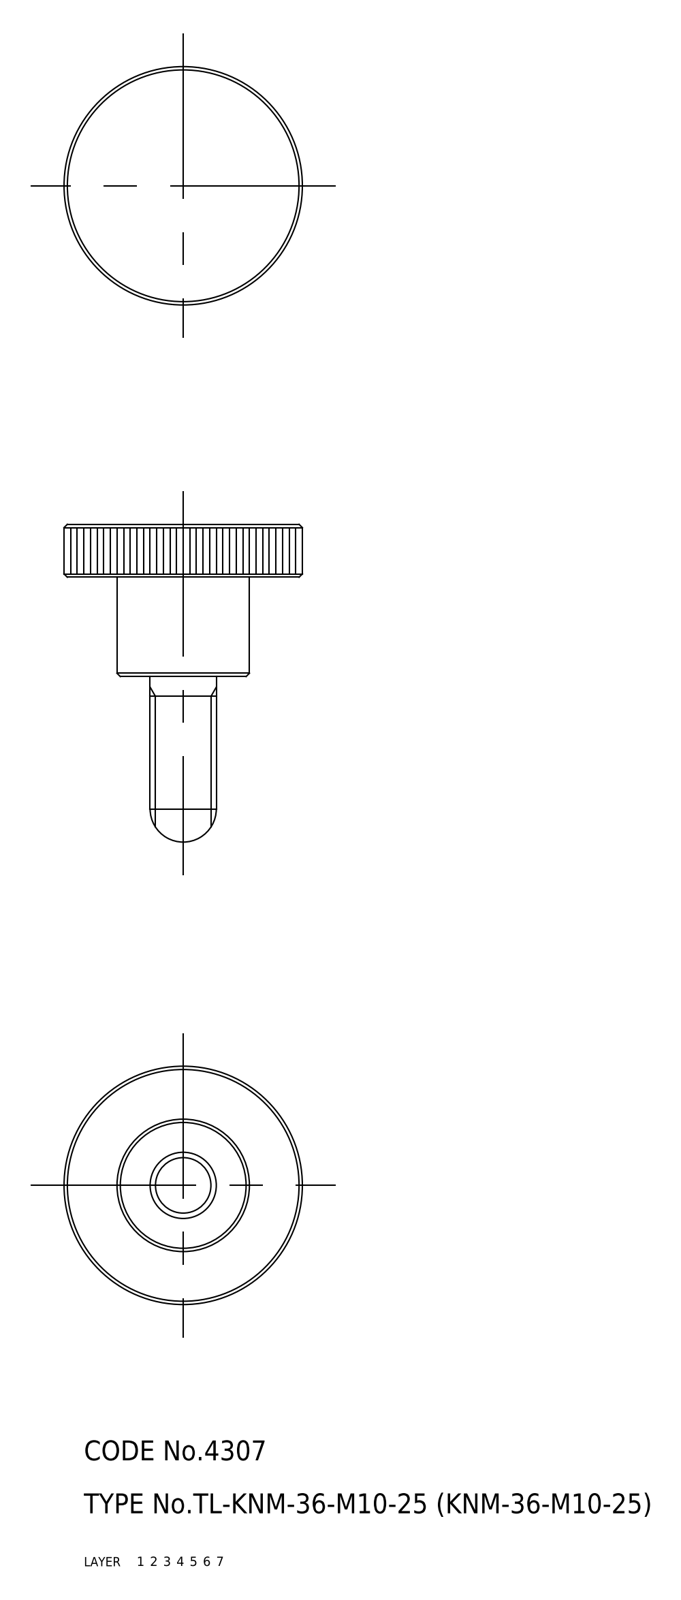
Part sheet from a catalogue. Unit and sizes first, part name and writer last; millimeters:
Units: millimetres
Overall size (bounding box): 48 × 36 × 36
Volume: 14 678 mm³ · Surface area: 4 505 mm²
Bodies: 1 solid, 16 faces (0 planar, 0 cylindrical, 16 other)
Part name (STEP PRODUCT): knob
STEP written by: CADfix (AUTOMOTIVE_DESIGN)
